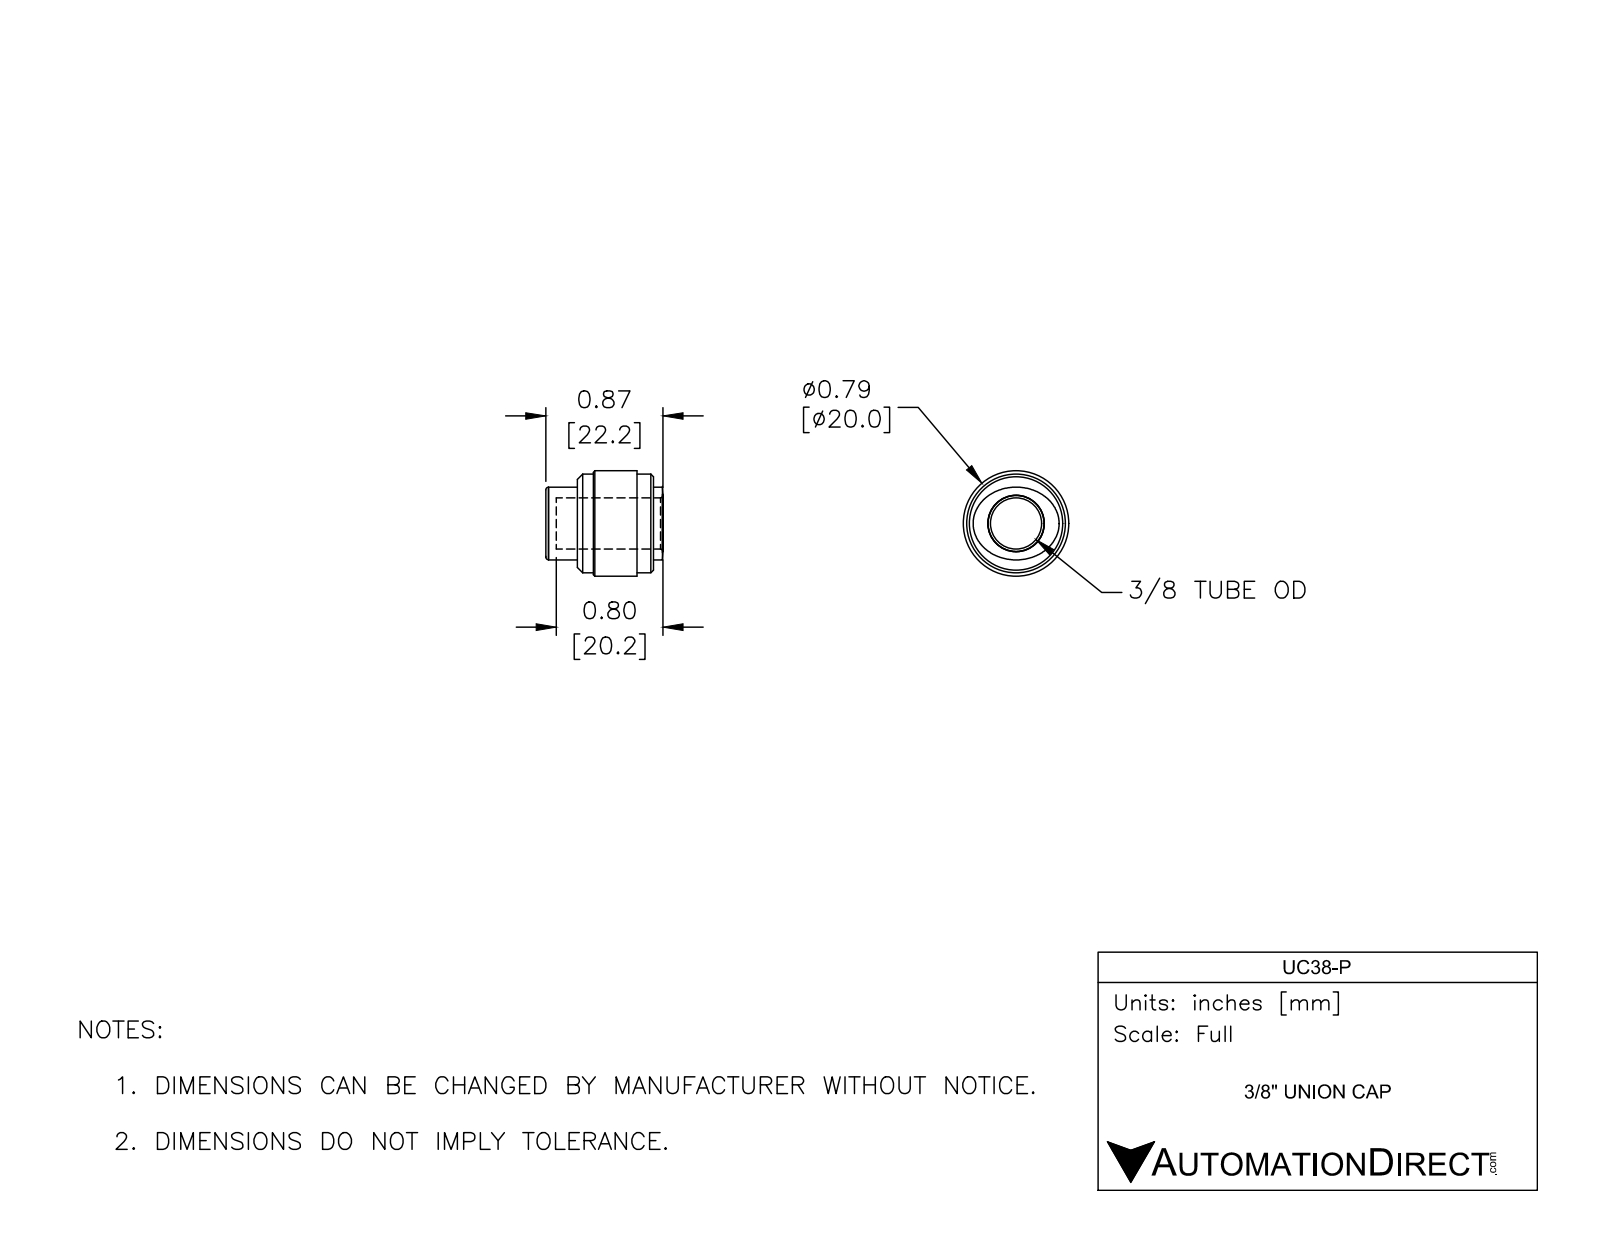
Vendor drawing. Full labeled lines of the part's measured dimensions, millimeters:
Part name (STEP PRODUCT): UC38-P
STEP written by: SolidWorks 2017 (AUTOMOTIVE_DESIGN)
Units: millimetres
Bodies: 1 solid, 33 faces (7 planar, 10 cylindrical, 16 other)
Overall size (bounding box): 22.2 × 20 × 20
Volume: 3 970 mm³ · Surface area: 2 385 mm²
Round holes (diameter × count): ⌀9.7 ×1
Round bosses / shafts (diameter × count): ⌀20 ×1, ⌀18.7 ×1, ⌀13.8 ×1
Main face-to-face distances: 2, 6, 4, 20.4, 18.4, 14.4, 17.3, 15.3, 11.3, 3.1
